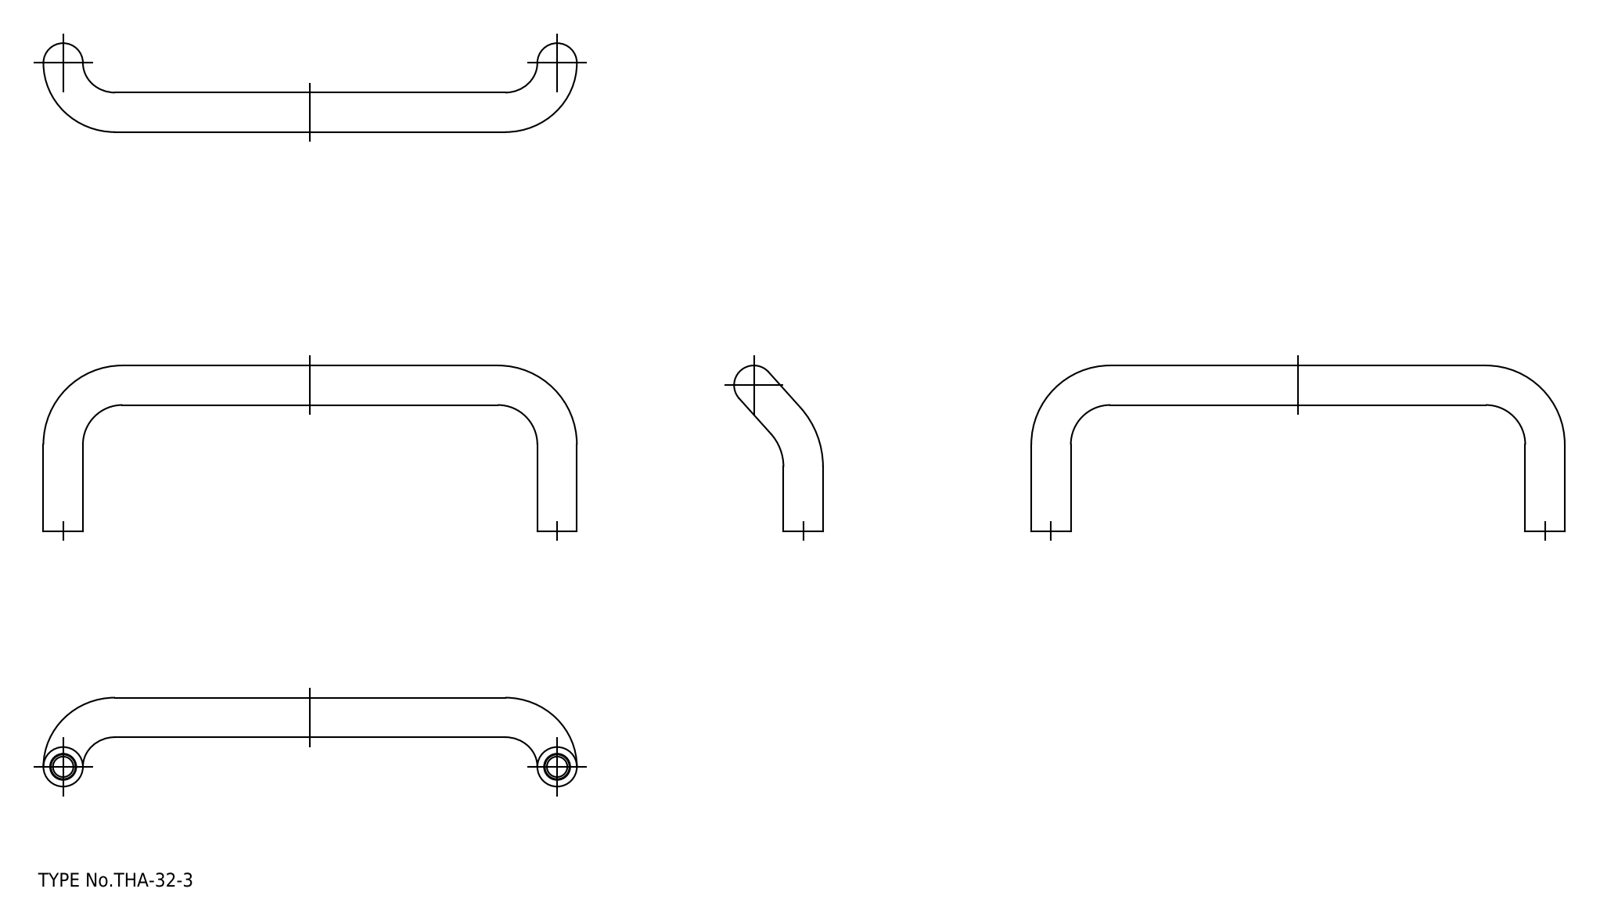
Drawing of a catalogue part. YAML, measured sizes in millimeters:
step_written_by: "spGate 17.5.2 (AUTOMOTIVE_DESIGN)"
units: millimeters
bodies: {solids: 1, faces: 30, planar: 4, cylindrical: 10, other: 16}
overall_size: [108, 33.5, 18]
volume: 7421
surface_area: 4322
round_holes:
  - {diameter: 5, count: 2}
round_bosses_or_shafts:
  - {diameter: 8, count: 3}
face_to_face_distances: [10]
hole_center_spacings: [100]
